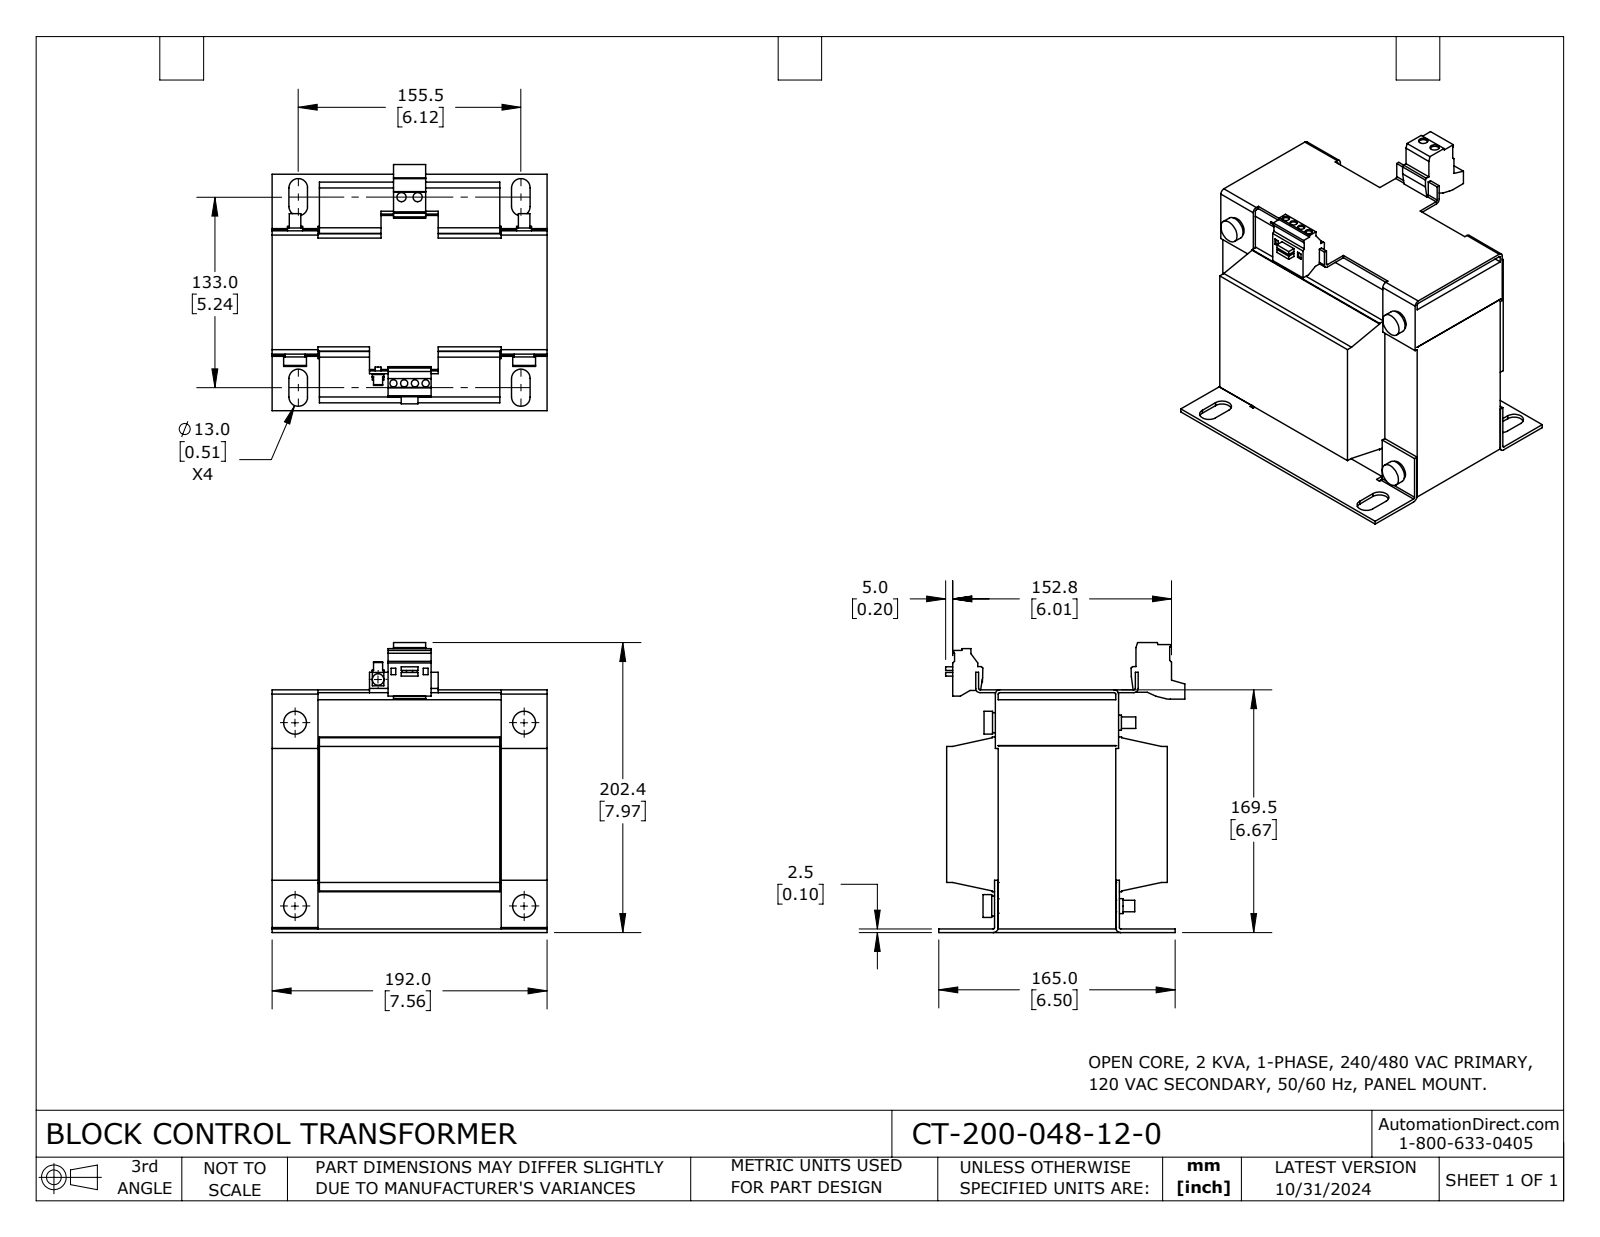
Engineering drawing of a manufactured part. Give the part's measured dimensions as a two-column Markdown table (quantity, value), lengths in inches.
| quantity | value |
| --- | --- |
| part name | CT-200-048-12-0 |
| STEP written by | SolidWorks 2023 (CONFIG_CONTROL_DESIGN) |
| units | inches |
| bodies | 1 solid, 336 faces (243 planar, 93 cylindrical, 0 other) |
| overall size | 7.969 × 7.559 × 6.764 |
| volume | 218.5 in³ |
| surface area | 495.5 in² |
| round holes (diameter × count) | 0.197 × 4, 0.252 × 2 |
| round bosses / shafts (diameter × count) | 0.315 × 5, 0.63 × 4, 0.551 × 4, 0.413 × 4, 0.394 × 2, 0.157 × 1 |
| partial cylindrical surfaces (radius × count) | 0.256 × 8, 0.039 × 6, 0.118 × 4, 0.138 × 2, 0.591 × 1 |
| main face-to-face distances | 1.26, 5.039, 6.299, 1.299, 6.26, 5.138, 1.417, 4.646, 0.098, 0.079 |
| hole center spacings | 0.295, 0.591, 5.119, 5.123, 5.131, 5.161, 0.443, 0.886 |
